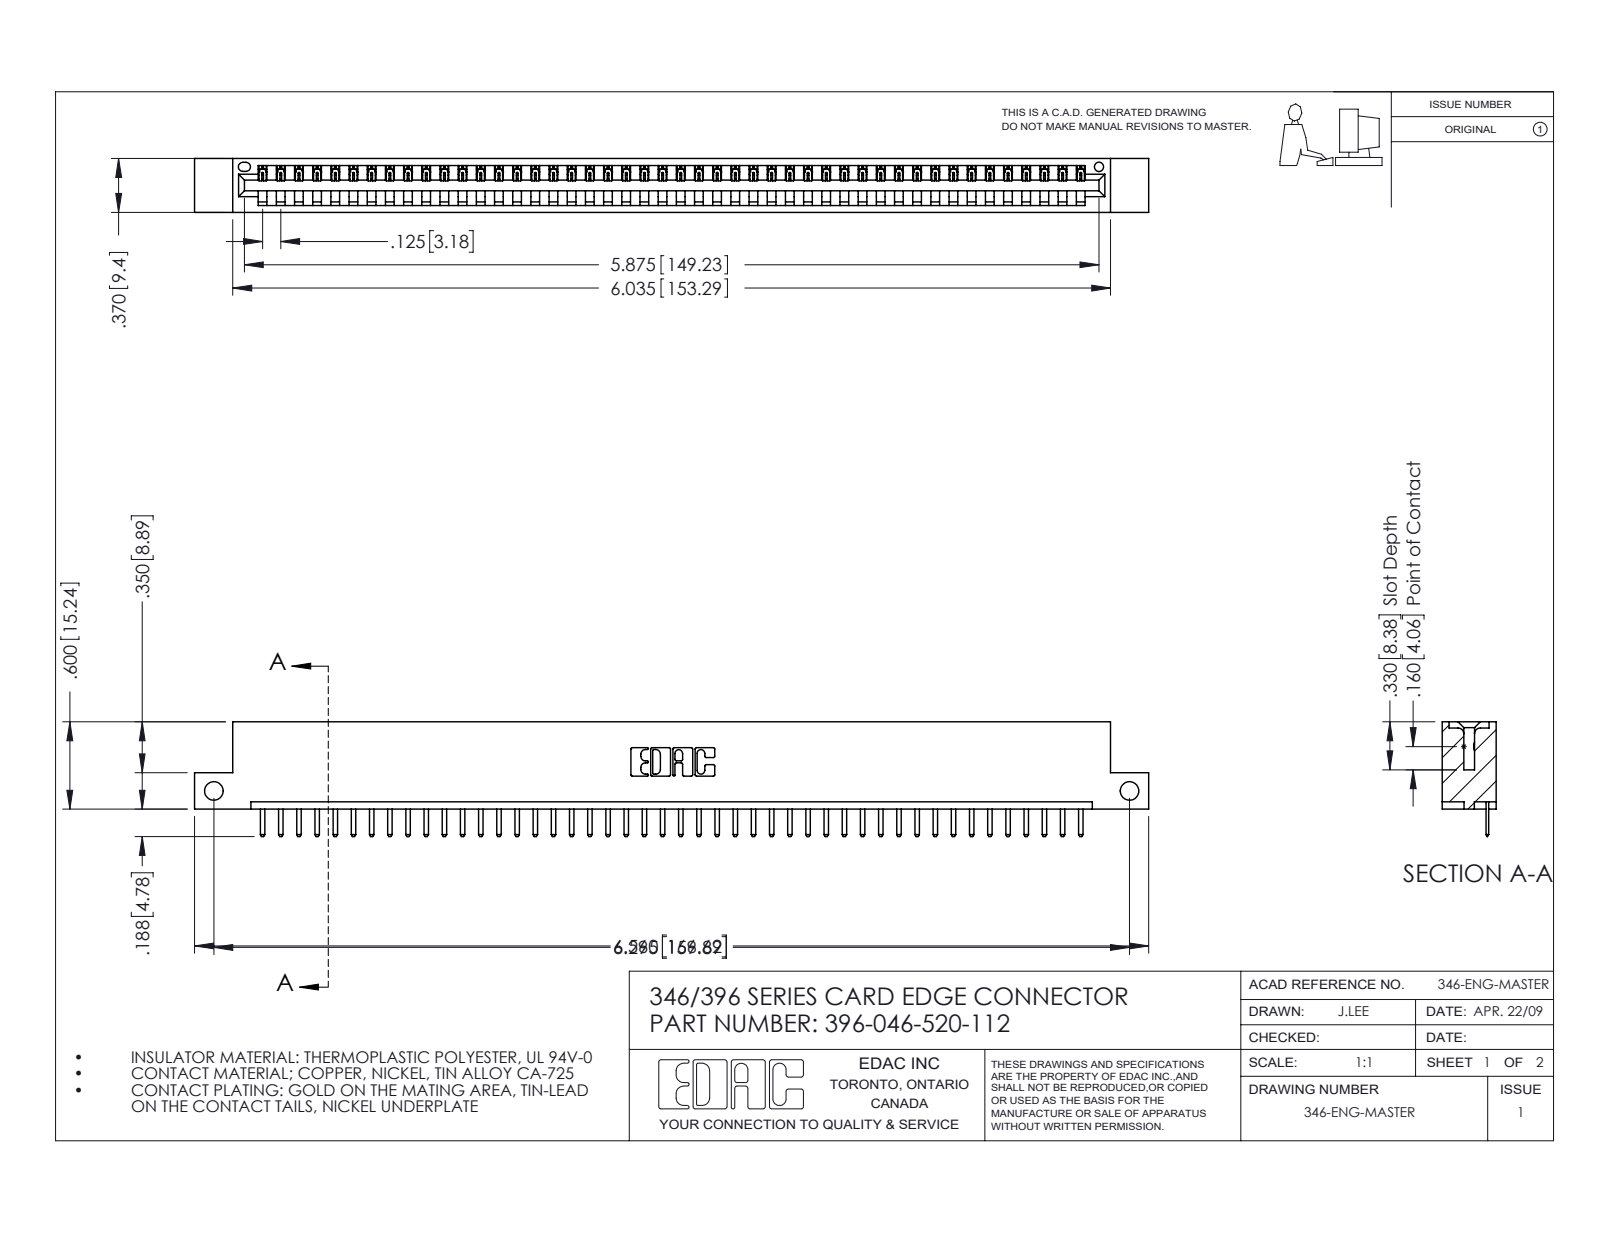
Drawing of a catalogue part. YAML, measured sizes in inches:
part_name: "396-046-520-112; 345-292-001_345-293-120; 346 Part_Flush Mounting Lugs - Side Mount"
step_written_by: "SolidWorks 2016 (CONFIG_CONTROL_DESIGN)"
units: inches
bodies: {solids: 47, faces: 2974, planar: 2008, cylindrical: 966, other: 0}
overall_size: [6.56, 0.788, 0.37]
volume: 0.962
surface_area: 29.68
round_holes:
  - {diameter: 0.128, count: 2}
  - {diameter: 0.064, count: 1}
partial_cylinders:
  - {radius: 0.01, count: 94}
  - {radius: 0.006, count: 92}
  - {radius: 0.01, count: 22}
  - {radius: 0.007, count: 6}
  - {radius: 0.031, count: 6}
  - {radius: 0.026, count: 3}
  - {radius: 0.031, count: 2}
  - {radius: 0.04, count: 2}
face_to_face_distances: [0.048, 0.322, 0.37, 0.25, 0.148, 0.222, 0.1, 0.174, 0.072, 0.298]
hole_center_spacings: [6.295]
